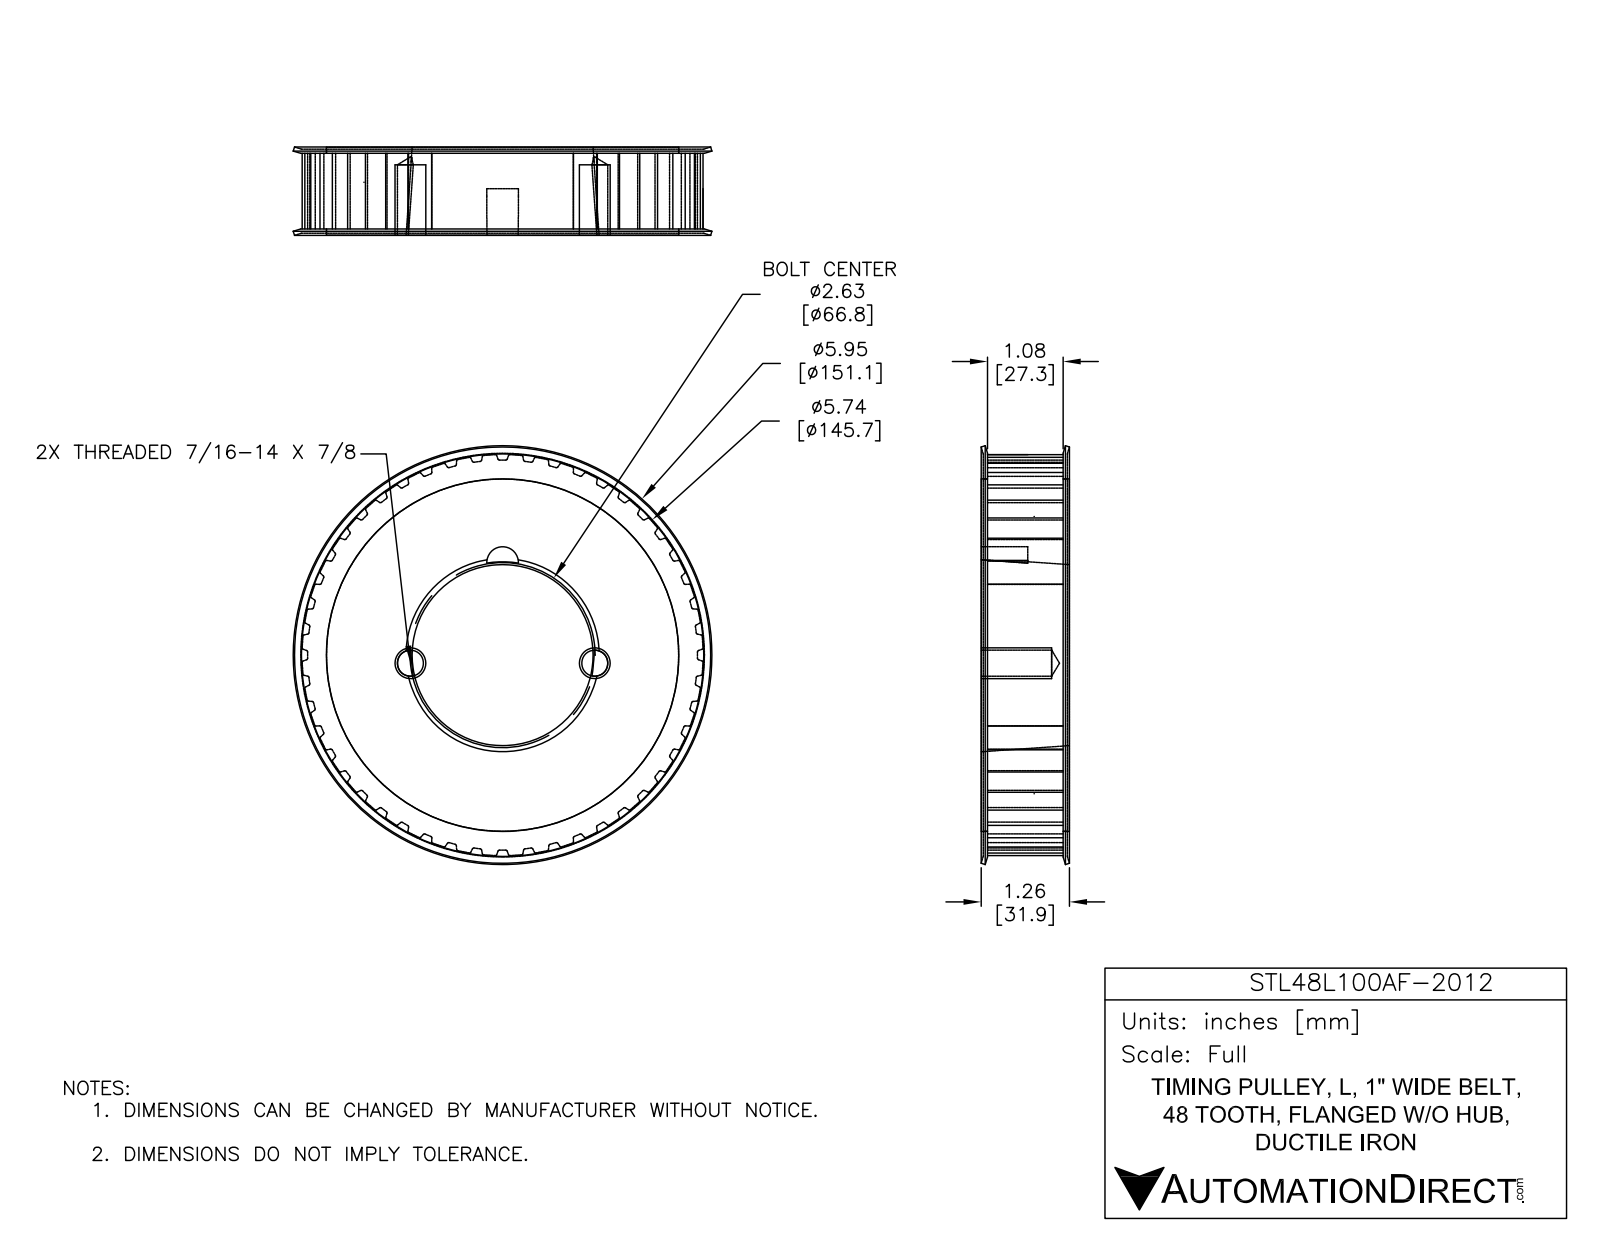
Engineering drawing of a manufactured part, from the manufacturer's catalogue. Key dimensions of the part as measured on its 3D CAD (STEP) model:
Part name (STEP PRODUCT): STL48L100AF-2012
STEP written by: SolidWorks 2018 (AUTOMOTIVE_DESIGN)
Units: millimetres
Bodies: 1 solid, 464 faces (153 planar, 293 cylindrical, 18 other)
Overall size (bounding box): 151.13 × 151.13 × 31.88
Volume: 395 968 mm³ · Surface area: 59 427 mm²
Round holes (diameter × count): ⌀127.1 ×1
Round bosses / shafts (diameter × count): ⌀127.01 ×1
Partial cylindrical surfaces — rounded edges, fillets, slot ends (radius × count): R0.38 ×96, R0.51 ×96, R4.7 ×2, R5.71 ×1, R72.39 ×1
Main face-to-face distances: 31.75, 0.7, 31.05, 30.35, 2.22, 29.53, 1.52, 28.83, 27.31, 45.25
